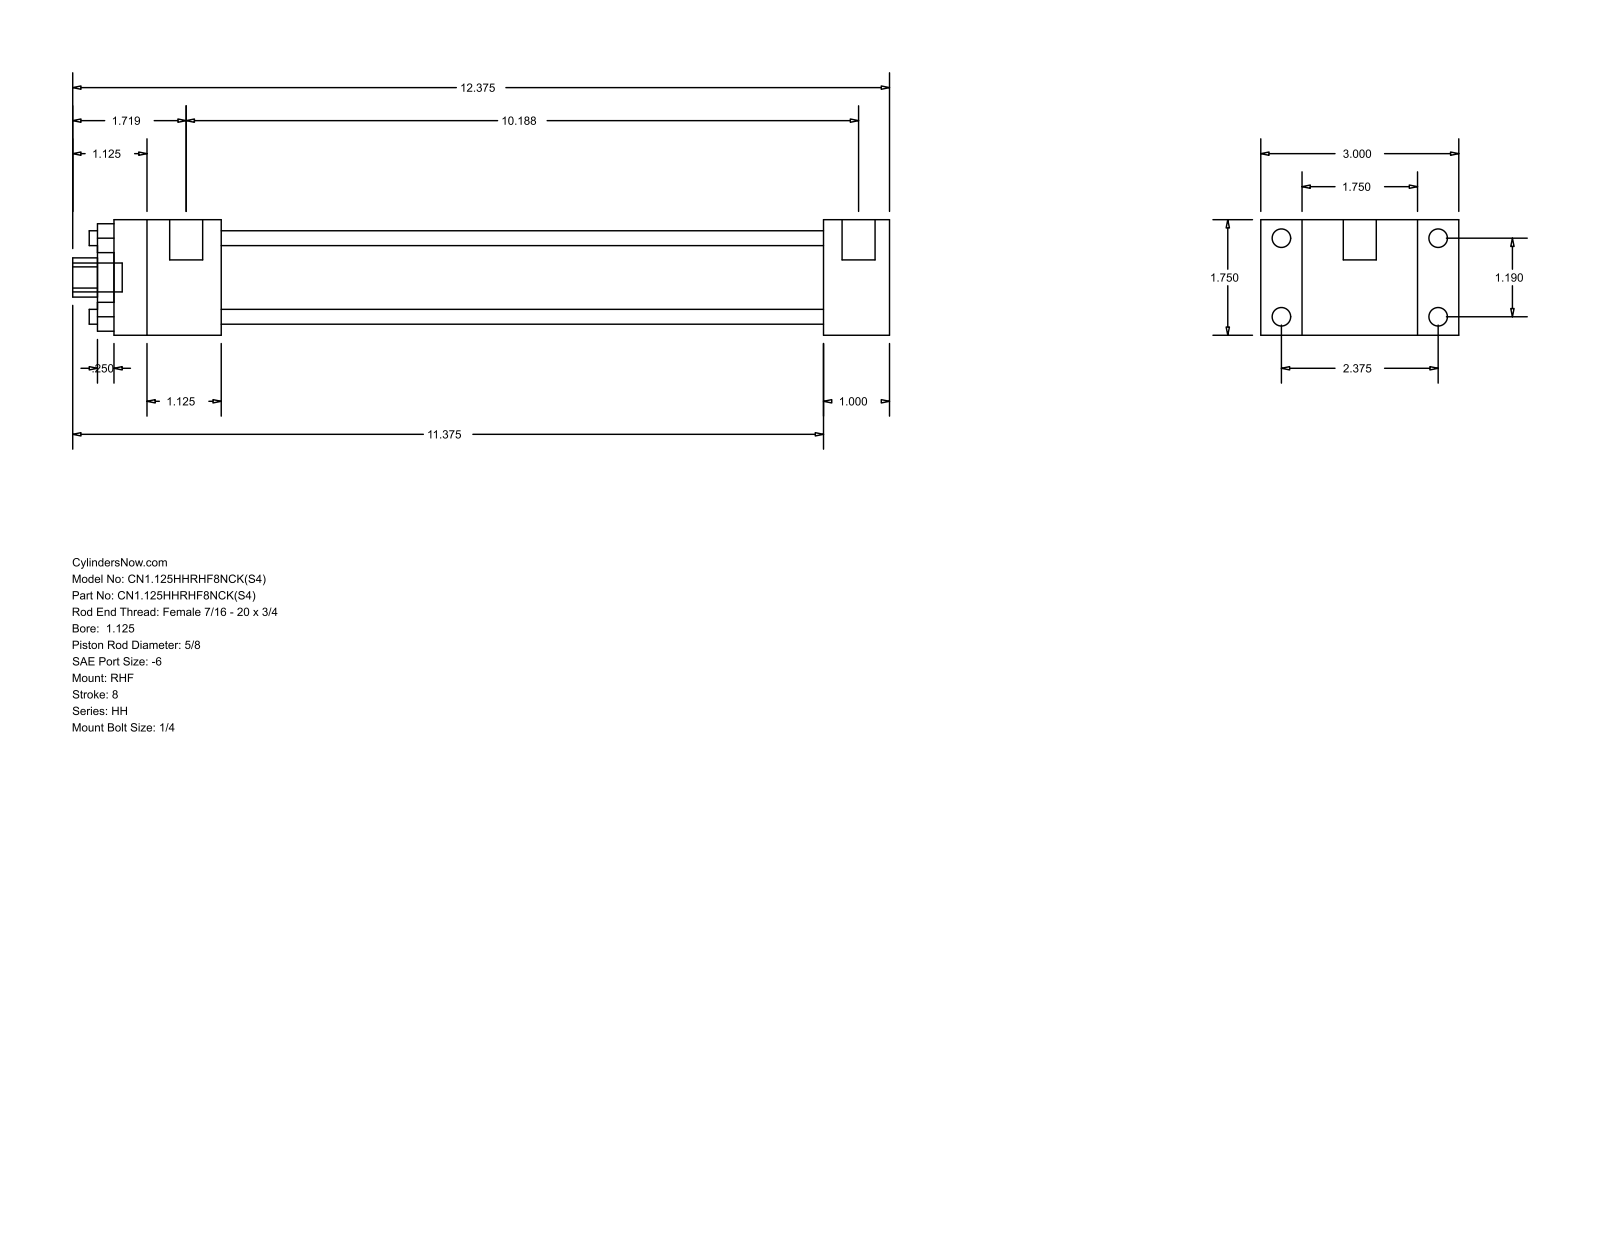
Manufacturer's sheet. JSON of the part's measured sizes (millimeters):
{"part_name": "HH_RHF__0112_0.625", "step_written_by": "GSSL Pune (CONFIG_CONTROL_DESIGN)", "units": "millimeters", "bodies": {"solids": 0, "faces": 88, "planar": 60, "cylindrical": 28, "other": 0}, "overall_size": [314.32, 76.2, 44.45], "round_holes": [[5.71, 4], [15.88, 1], [28.57, 1], [34.92, 1]], "round_bosses_or_shafts": [[7.14, 4], [5.56, 4], [12.7, 2], [11.11, 1]], "partial_cylinders_radius": [[7.54, 1]], "face_to_face_distances": [44.46, 15.87, 60.33, 25.39, 76.2, 231.78, 257.17, 41.27, 273.05, 298.44], "hole_center_spacings": [21.37, 30.22, 42.74]}
